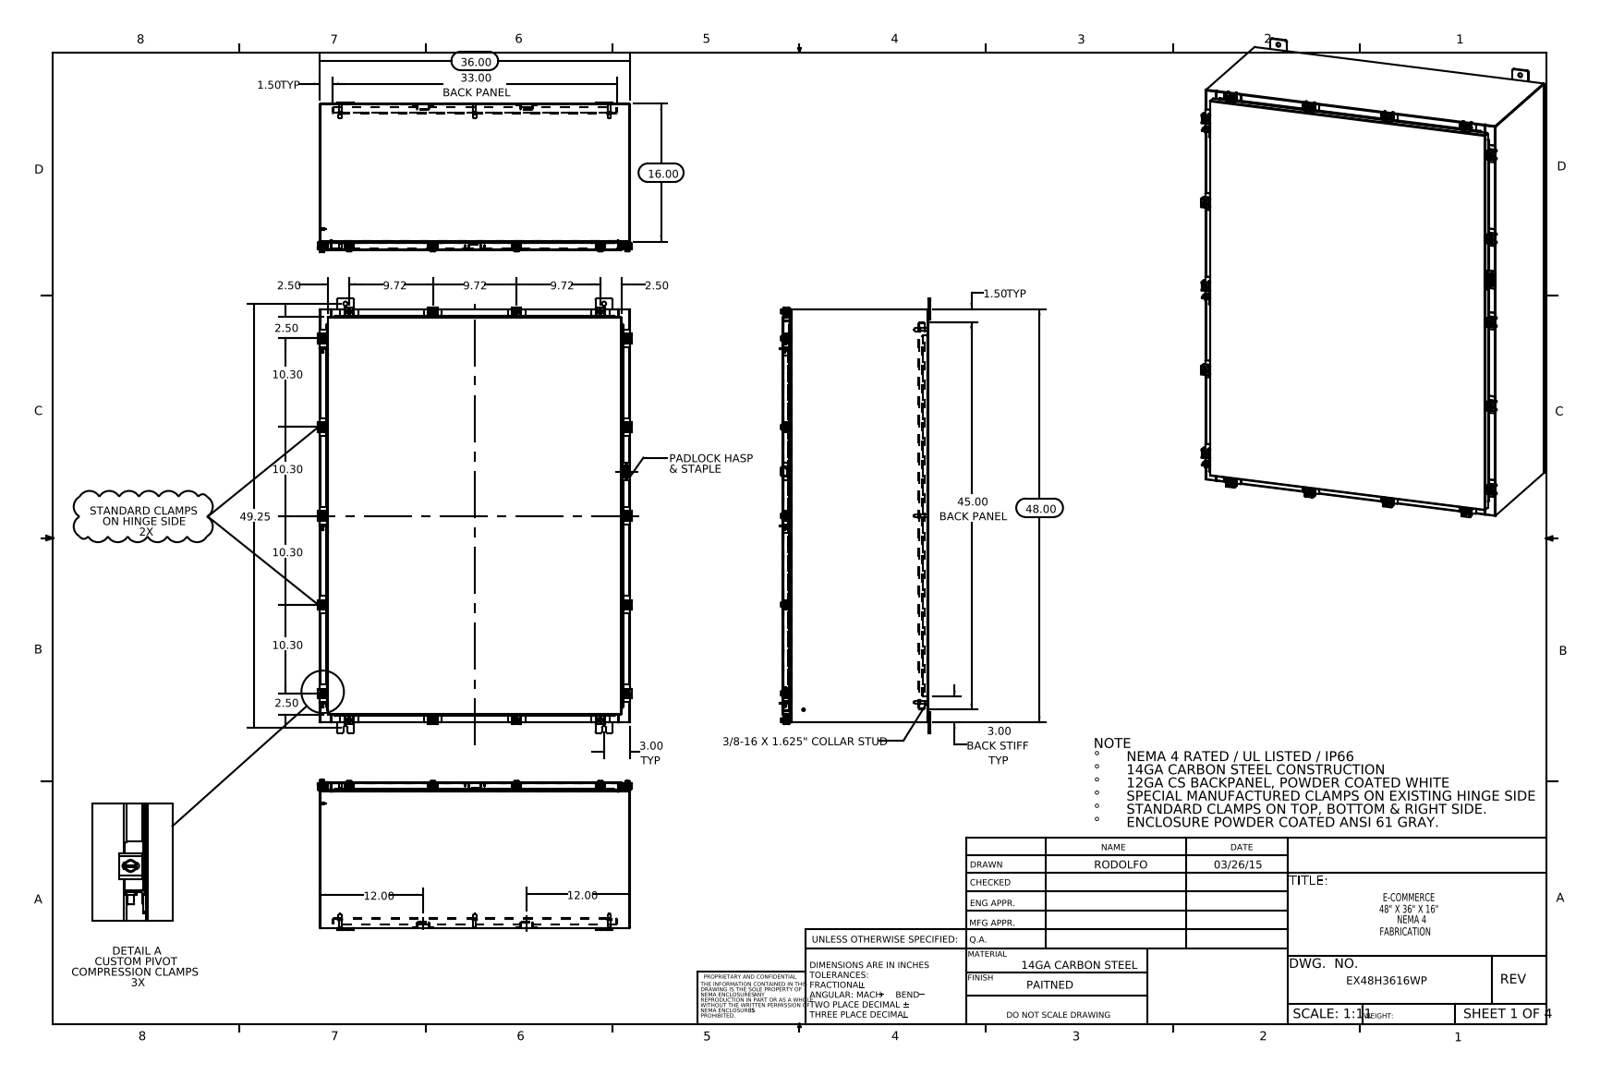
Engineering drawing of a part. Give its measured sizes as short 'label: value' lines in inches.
name: EX48H3616WP Clamp Bracket; EX48H3616WP Standard Clamps; N-WMT04X30402202210-00 Clamp Top; EX48H3616WP Cover (+8 more)
written by: SolidWorks 2014 (CONFIG_CONTROL_DESIGN)
unit: in
bodies: 126 solids, 3106 faces (1613 planar, 1195 cylindrical, 298 other)
size: 50.5 × 36.421 × 17.453
volume: 698.7 in³; area: 17 479 in²
holes: 18× ⌀0.213, 18× ⌀0.26, 12× ⌀0.5, 7× ⌀0.25, 1× ⌀0.125
bosses: 18× ⌀0.5, 18× ⌀0.25, 15× ⌀0.399, 8× ⌀0.625, 8× ⌀0.375, 8× ⌀0.33, 6× ⌀0.157, 6× ⌀0.14
rounds: 76× R0.06, 38× R0.013, 36× R0.141, 34× R0.088, 33× R0.12, 27× R0.09, 25× R0.05, 24× R0.145
face distances: 0.075, 16.9, 16.826, 16.975, 0.104, 35.925, 1, 1.075, 15.826, 15.9
hole spacings: 1.969, 2.347, 4.44, 13.972, 14.728, 16.126, 16.624, 17.756
